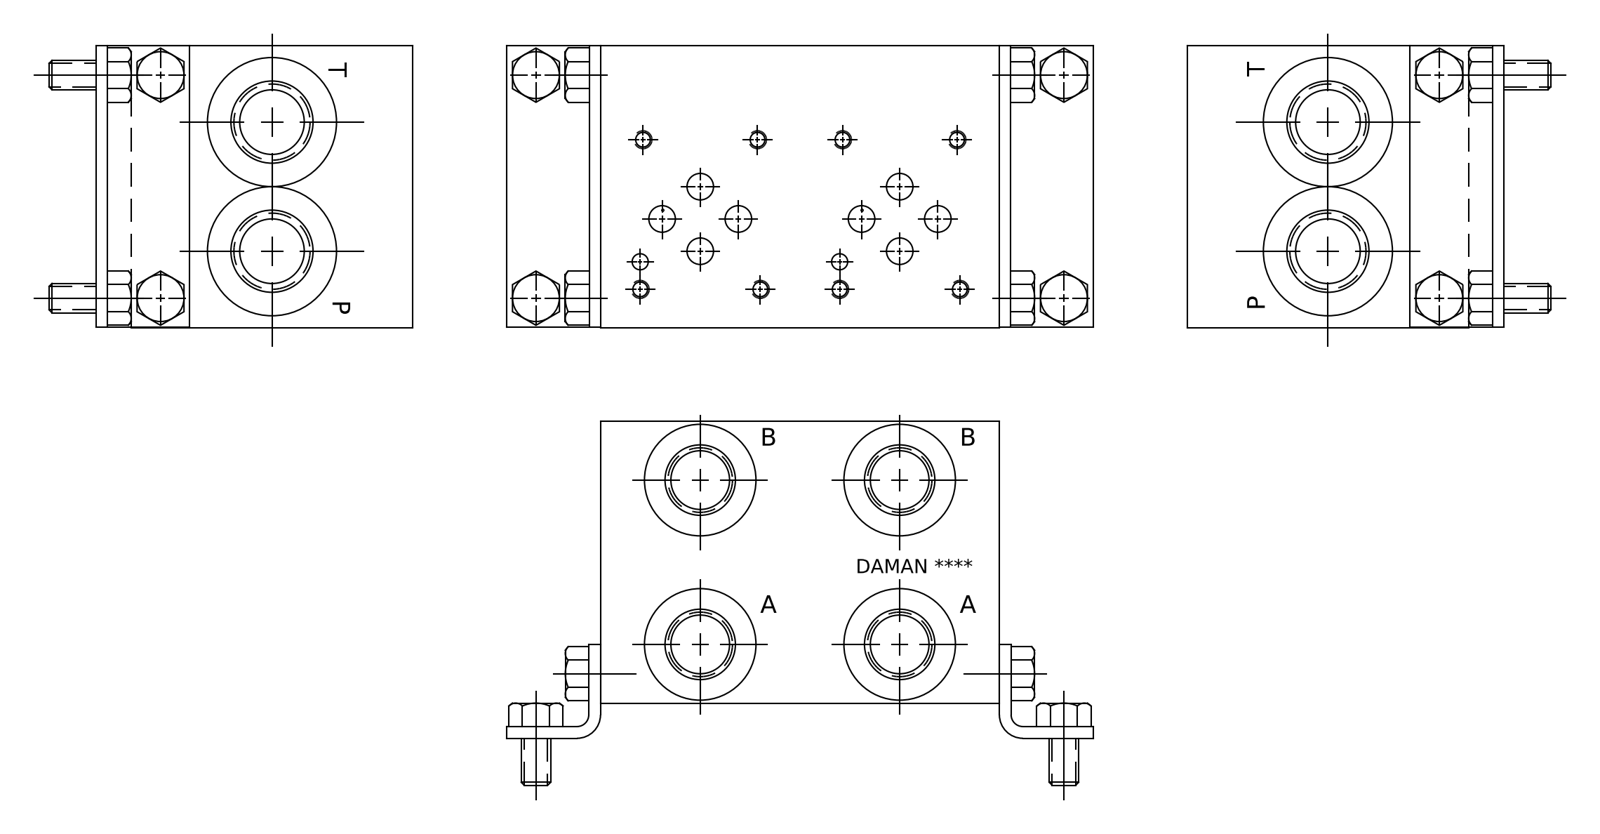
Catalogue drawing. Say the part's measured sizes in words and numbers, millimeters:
The part is named "C:\\\\Program Files\\\\PARO\\\\Hydroman 800\\\\Export\\\\AD03P022S_PA". Its 3-D file was written by "Autodesk Inventor 2012 (AUTOMOTIVE_DESIGN)". It is 1 solid with 114 faces: 22 planar, 54 cylindrical and 38 other. Overall it measures 107.95 by 76.2 by 76.2 millimeters. Its volume is 561 029 cubic millimeters and its surface area 60 116 square millimeters. Round holes: 8 of diameter 3.78, 6 of diameter 7.14, 4 of diameter 14.3, 4 of diameter 17.5, 4 of diameter 20.6, 4 of diameter 30.25, 2 of diameter 3.96, 2 of diameter 6.35, 2 of diameter 6.53, 2 of diameter 15.88, 2 of diameter 20.45, 2 of diameter 23.9. The main face-to-face distances are 76.2, 107.95, 0.79, 107.16, 75.41, 106.37, 3.28, 2.49, 104.67, 103.88. The hole center spacings are 53.98, 53.97, 19.95, 22.05, 33.55, 40.49, 51.45, 7.49.
